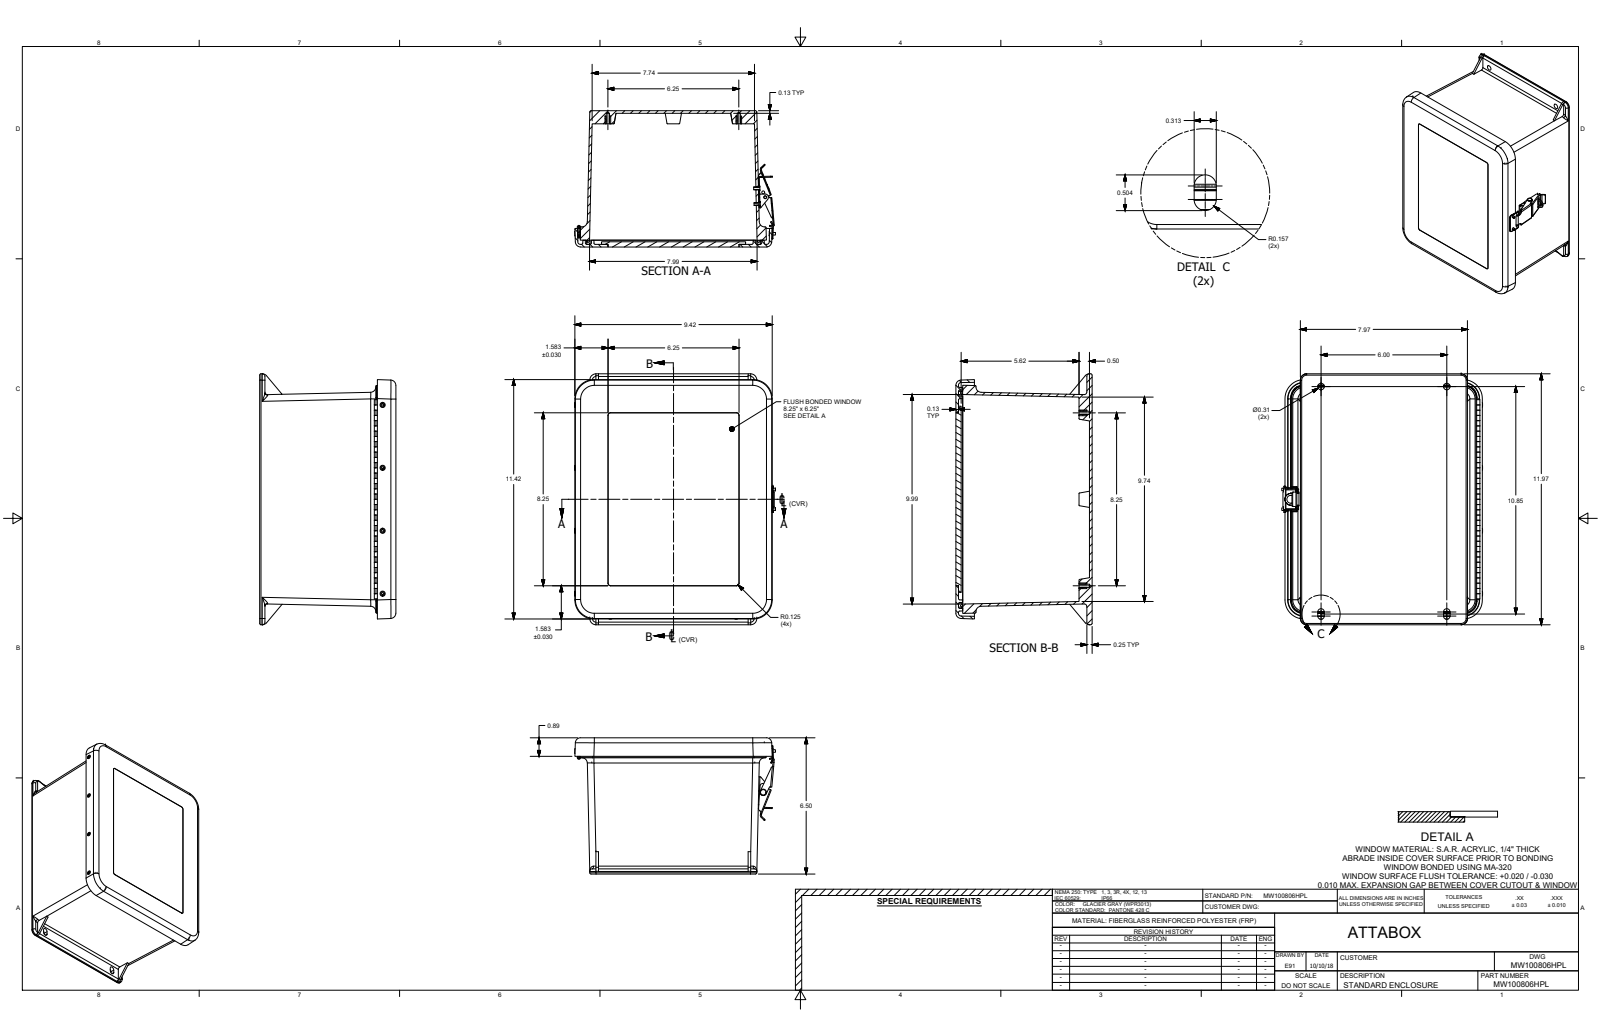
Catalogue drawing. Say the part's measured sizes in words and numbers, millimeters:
The part is named "MW100806HPL". Its 3-D file was written by "SolidWorks 2018 (AUTOMOTIVE_DESIGN)". It is 37 solids with 1199 faces: 465 planar, 466 cylindrical and 268 other. Overall it measures 303.9 by 244.8 by 165.1 millimeters. Its volume is 1 380 000 cubic millimeters and its surface area 683 200 square millimeters. Round holes: 14 of diameter 3.6, 12 of diameter 2.6, 12 of diameter 3.9, 12 of diameter 4, 8 of diameter 3.3, 5 of diameter 9.5, 2 of diameter 3.3, 2 of diameter 3.4, 2 of diameter 8, 1 of diameter 2.2, 1 of diameter 3.4. Round bosses or shafts: 12 of diameter 6.9, 7 of diameter 3.2, 5 of diameter 3.2, 1 of diameter 7.6, 1 of diameter 4.3, 1 of diameter 3.9, 1 of diameter 3.9, 1 of diameter 3. Partial cylindrical surfaces (rounded edges, fillets, slot ends): 26 of radius 0.8, 26 of radius 3.2, 20 of radius 1.6, 20 of radius 1.6, 16 of radius 1, 14 of radius 1.6, 12 of radius 0.4, 12 of radius 7.6. The main face-to-face distances are 158.7, 3.2, 165.1, 3.1, 3.1, 6.4, 161.9, 155.5, 3.2, 161.9. The hole center spacings are 152.4, 76.2, 63.5, 23.8, 88.9, 215.9, 228.6, 19.1.
